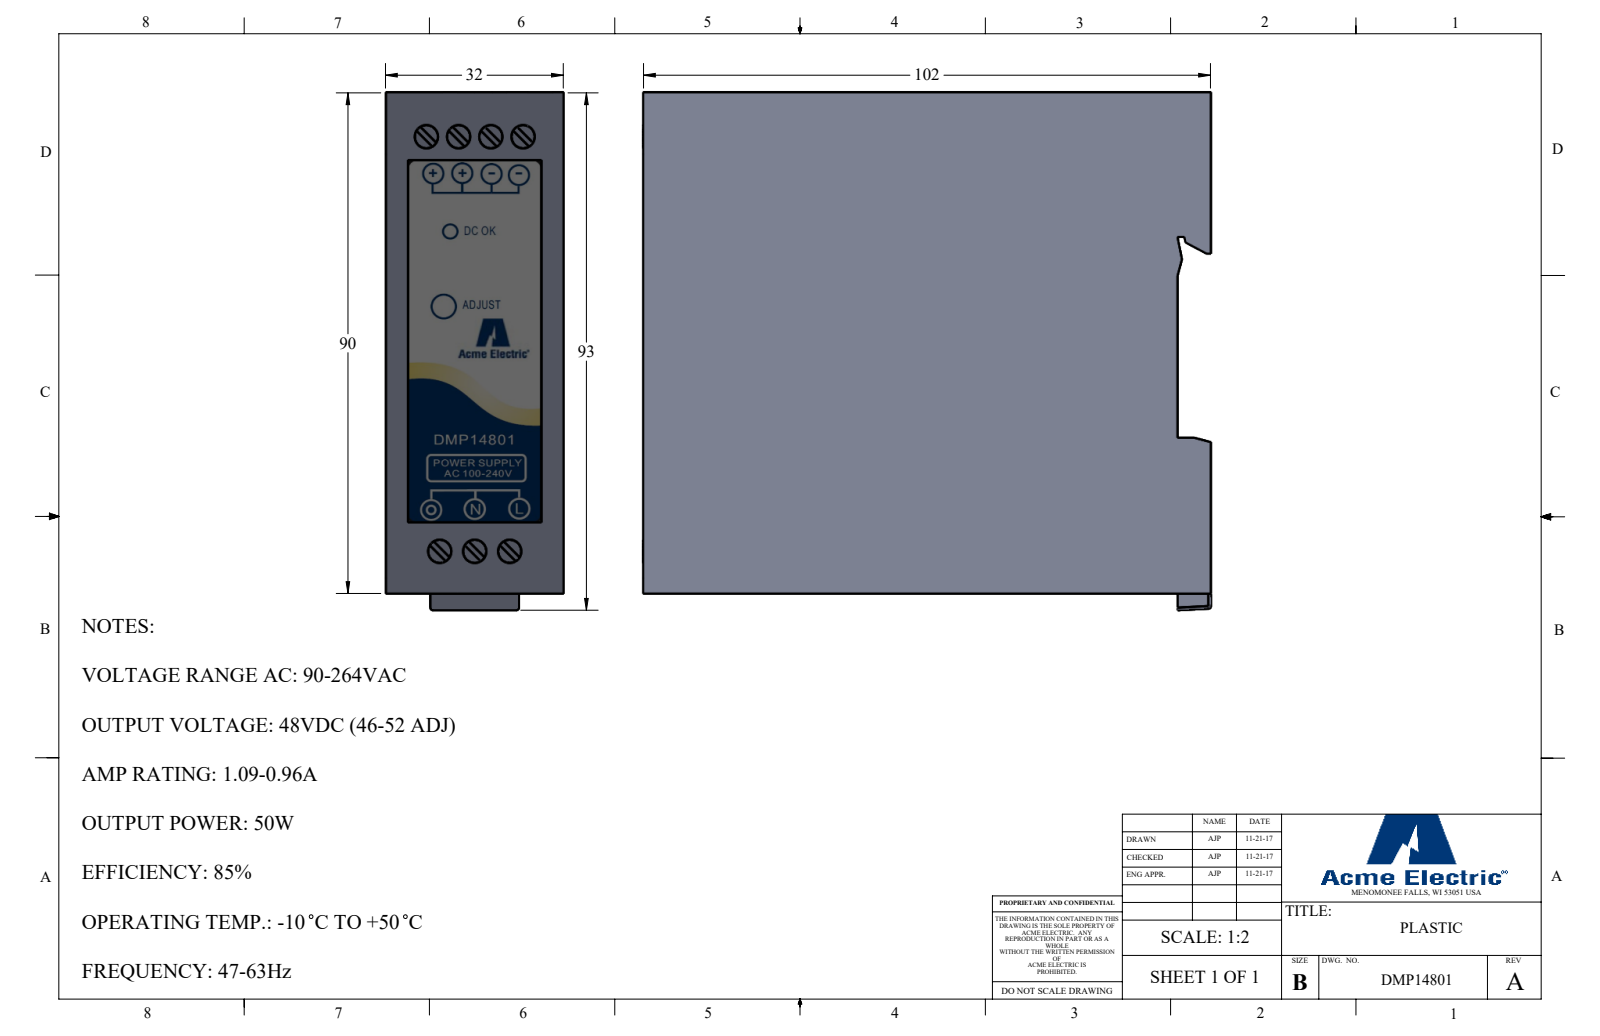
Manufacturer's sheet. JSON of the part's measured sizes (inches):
{"part_name": "DMP14801", "step_written_by": "SolidWorks 2017 (AUTOMOTIVE_DESIGN)", "units": "inches", "bodies": {"solids": 1, "faces": 77, "planar": 56, "cylindrical": 19, "other": 2}, "overall_size": [4.016, 3.661, 1.26], "volume_in3": 17.54, "surface_area_in2": 48.01, "round_holes": [[0.165, 7]], "partial_cylinders_radius": [[0.02, 5]], "face_to_face_distances": [1.26, 3.543, 4.016, 0.236, 3.78, 1.102, 2.441, 0.039, 3.976, 3.74], "hole_center_spacings": [0.228, 0.248, 0.457, 2.931, 2.931, 2.932, 2.949, 2.952]}
